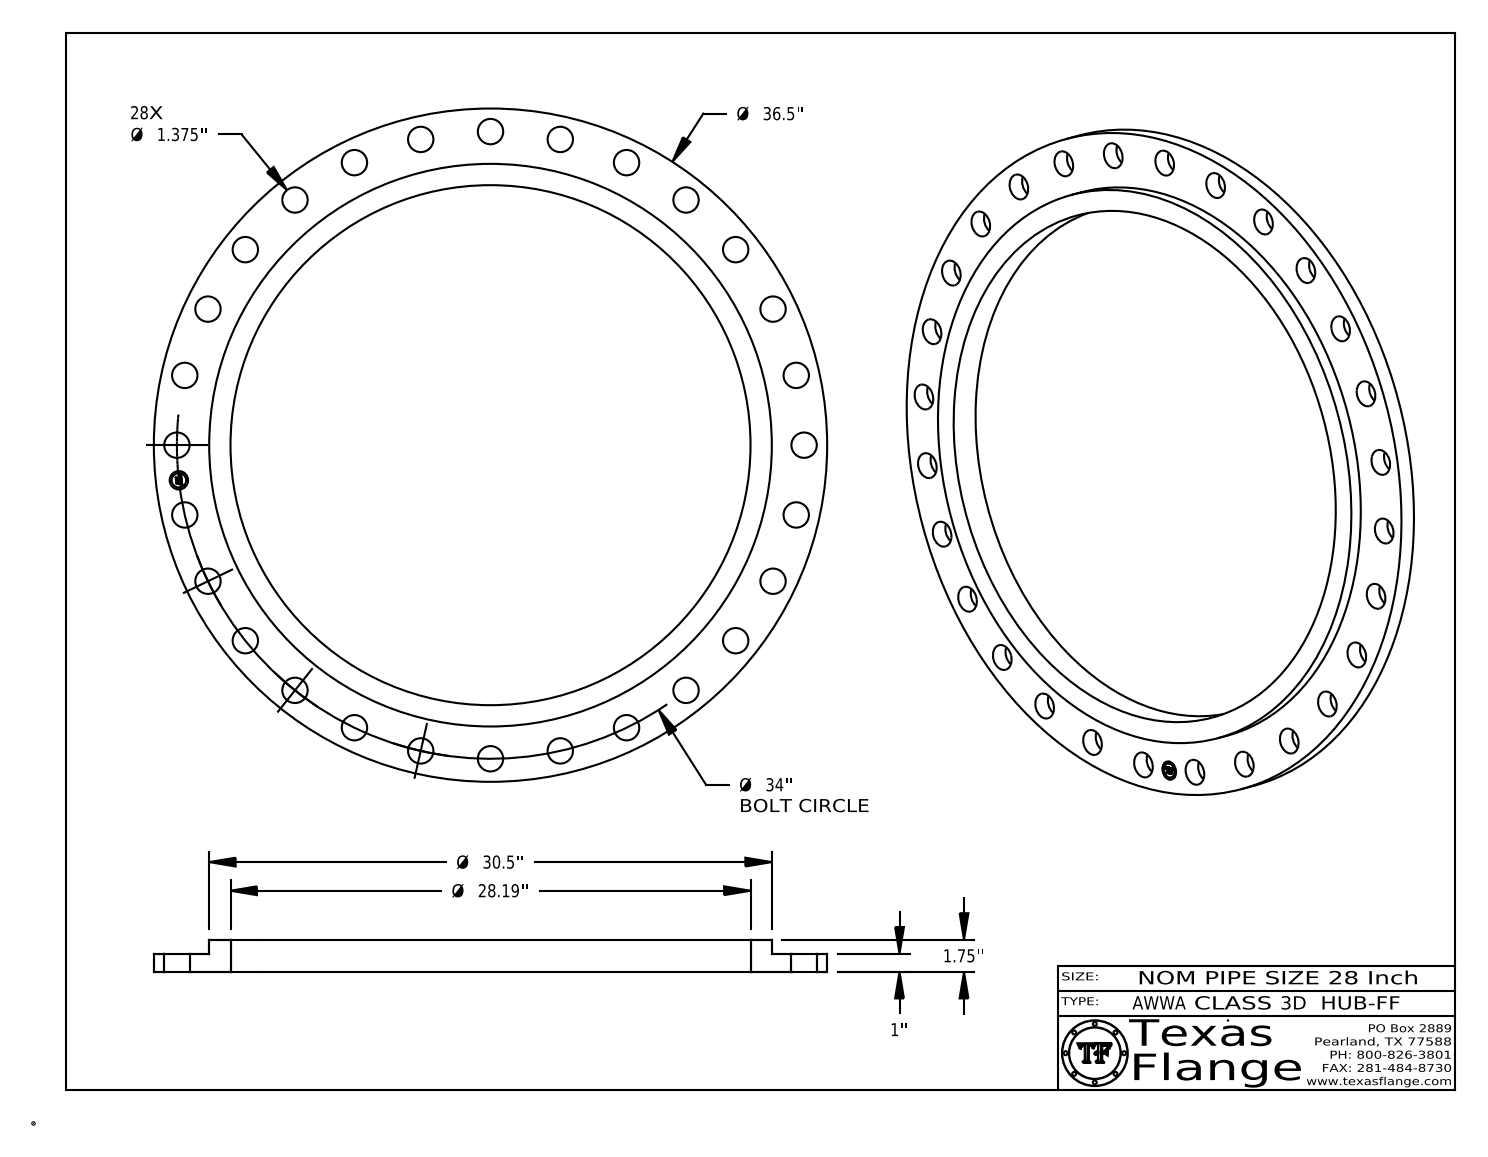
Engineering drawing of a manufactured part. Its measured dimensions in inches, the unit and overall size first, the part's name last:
Units: inches
Overall size (bounding box): 36.5 × 36.5 × 1.75
Round holes (diameter × count): ⌀1.375 ×28, ⌀1 ×1, ⌀28.19 ×1
Round bosses / shafts (diameter × count): ⌀0.061 ×8, ⌀36.5 ×1, ⌀30.5 ×1, ⌀0.788 ×1
Main face-to-face distances: 1, 1.75, 0.75, 0.015, 0.985, 0.765, 0.298, 0.293, 0.054, 0.193
Hole centre spacings: 3.807, 7.566, 30.633, 33.786, 17, 11.23, 18.089, 21.198
Volume: 460.5 in³ · Surface area: 1 224 in²
Bodies: 1 solid, 450 faces (368 planar, 82 cylindrical, 0 other)
Part name (STEP PRODUCT): AWWA Class 3D-HUB-FF
STEP written by: CATIA V5 STEP AP214 (AUTOMOTIVE_DESIGN)
